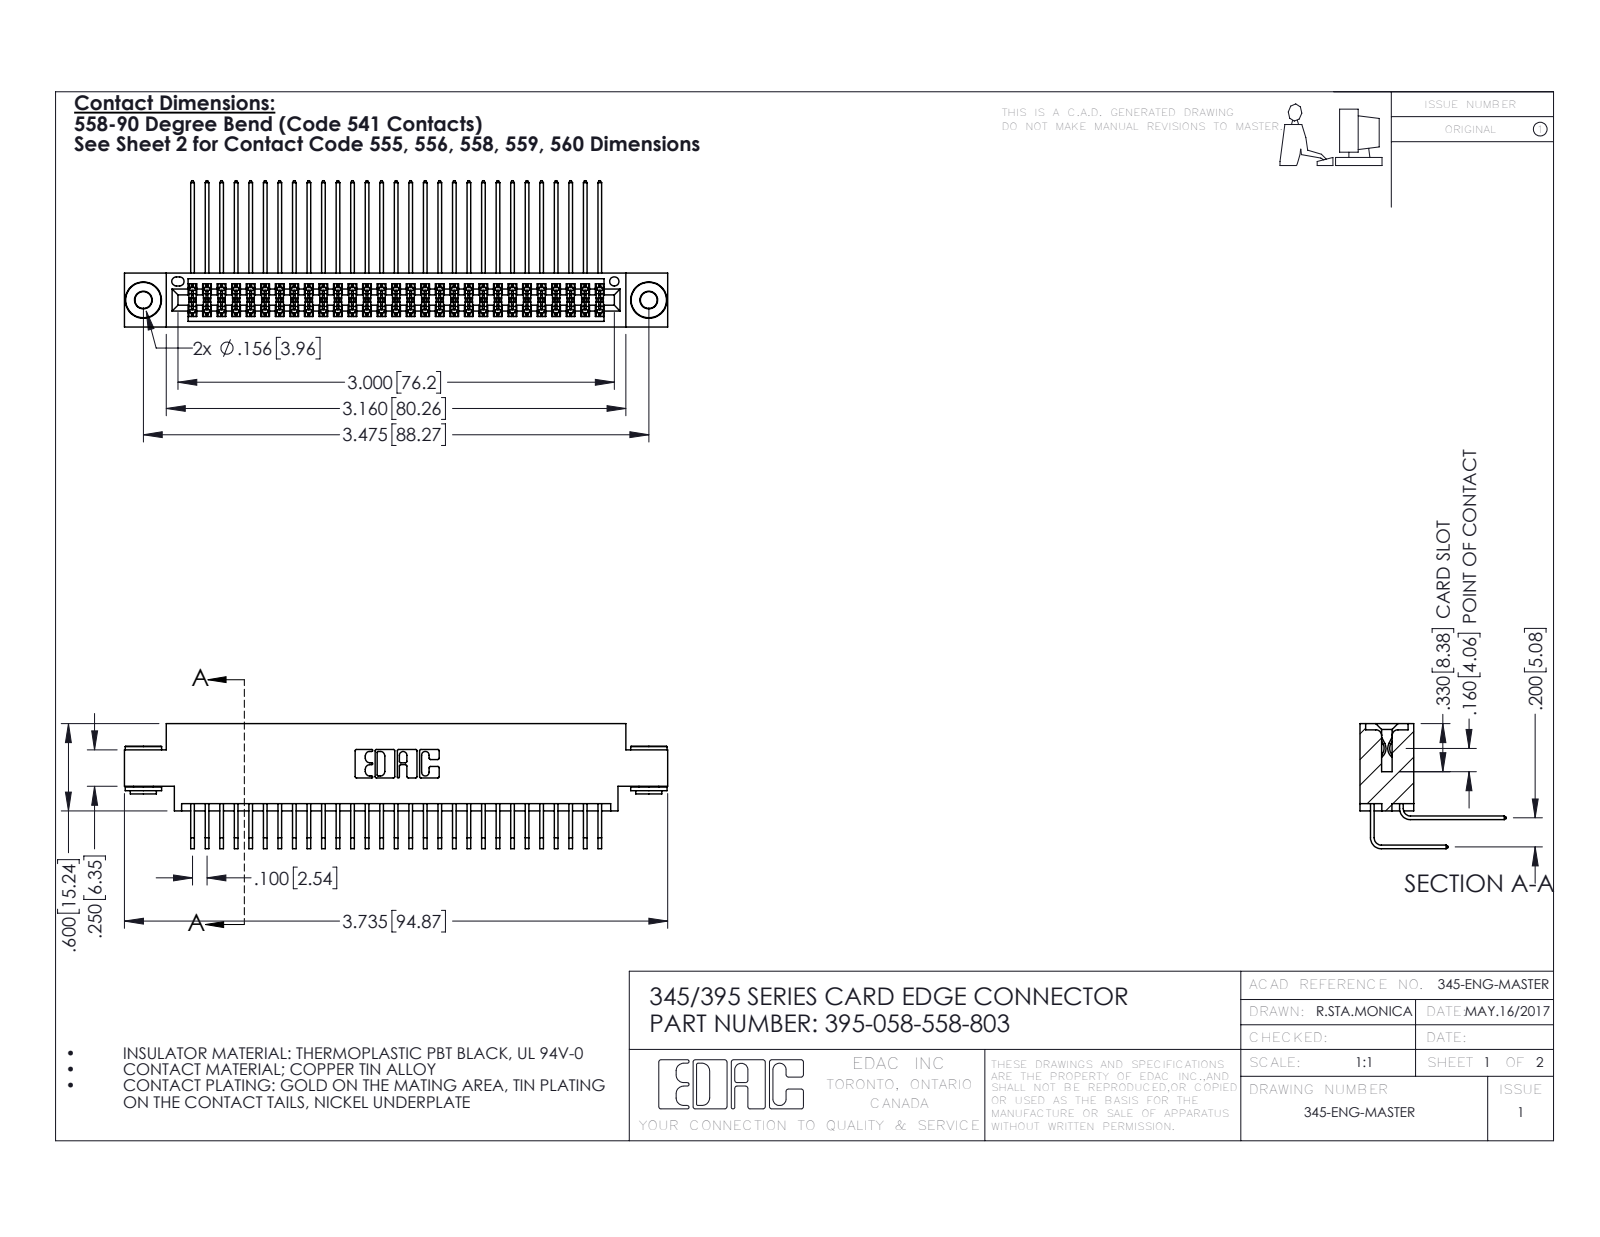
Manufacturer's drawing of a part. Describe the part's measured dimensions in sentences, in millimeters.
The part is named "345-250-002_345-250-002-102; 345 Part_0.170 Offset - 0.156 Dia-TH; 345-292-001_558 Tail - 2; 345-292-001_558 559 Tail - 1 (+1 more)". Its 3-D file was written by "SolidWorks 2016 (CONFIG_CONTROL_DESIGN)". It is 61 solids with 3184 faces: 2124 planar, 1052 cylindrical and 8 other. Overall it measures 94.9 by 25.5 by 21.8 millimeters. Its volume is 9 340 cubic millimeters and its surface area 15 470 square millimeters. Round holes: 2 of diameter 2.9, 2 of diameter 4, 1 of diameter 1.6. Round bosses or shafts: 2 of diameter 6.4, 2 of diameter 4.6, 2 of diameter 3.5. Partial cylindrical surfaces (rounded edges, fillets, slot ends): 88 of radius 0.2, 22 of radius 0.3, 6 of radius 0.2, 6 of radius 0.8, 3 of radius 0.7, 2 of radius 0.4, 2 of radius 0.5, 2 of radius 0.6. The main face-to-face distances are 1.8, 7.6, 5.1, 9.4, 2.5, 6.9, 0.6, 5.7, 4.4, 0.6. The hole center spacings are 6.9, 82.3, 88.3.
